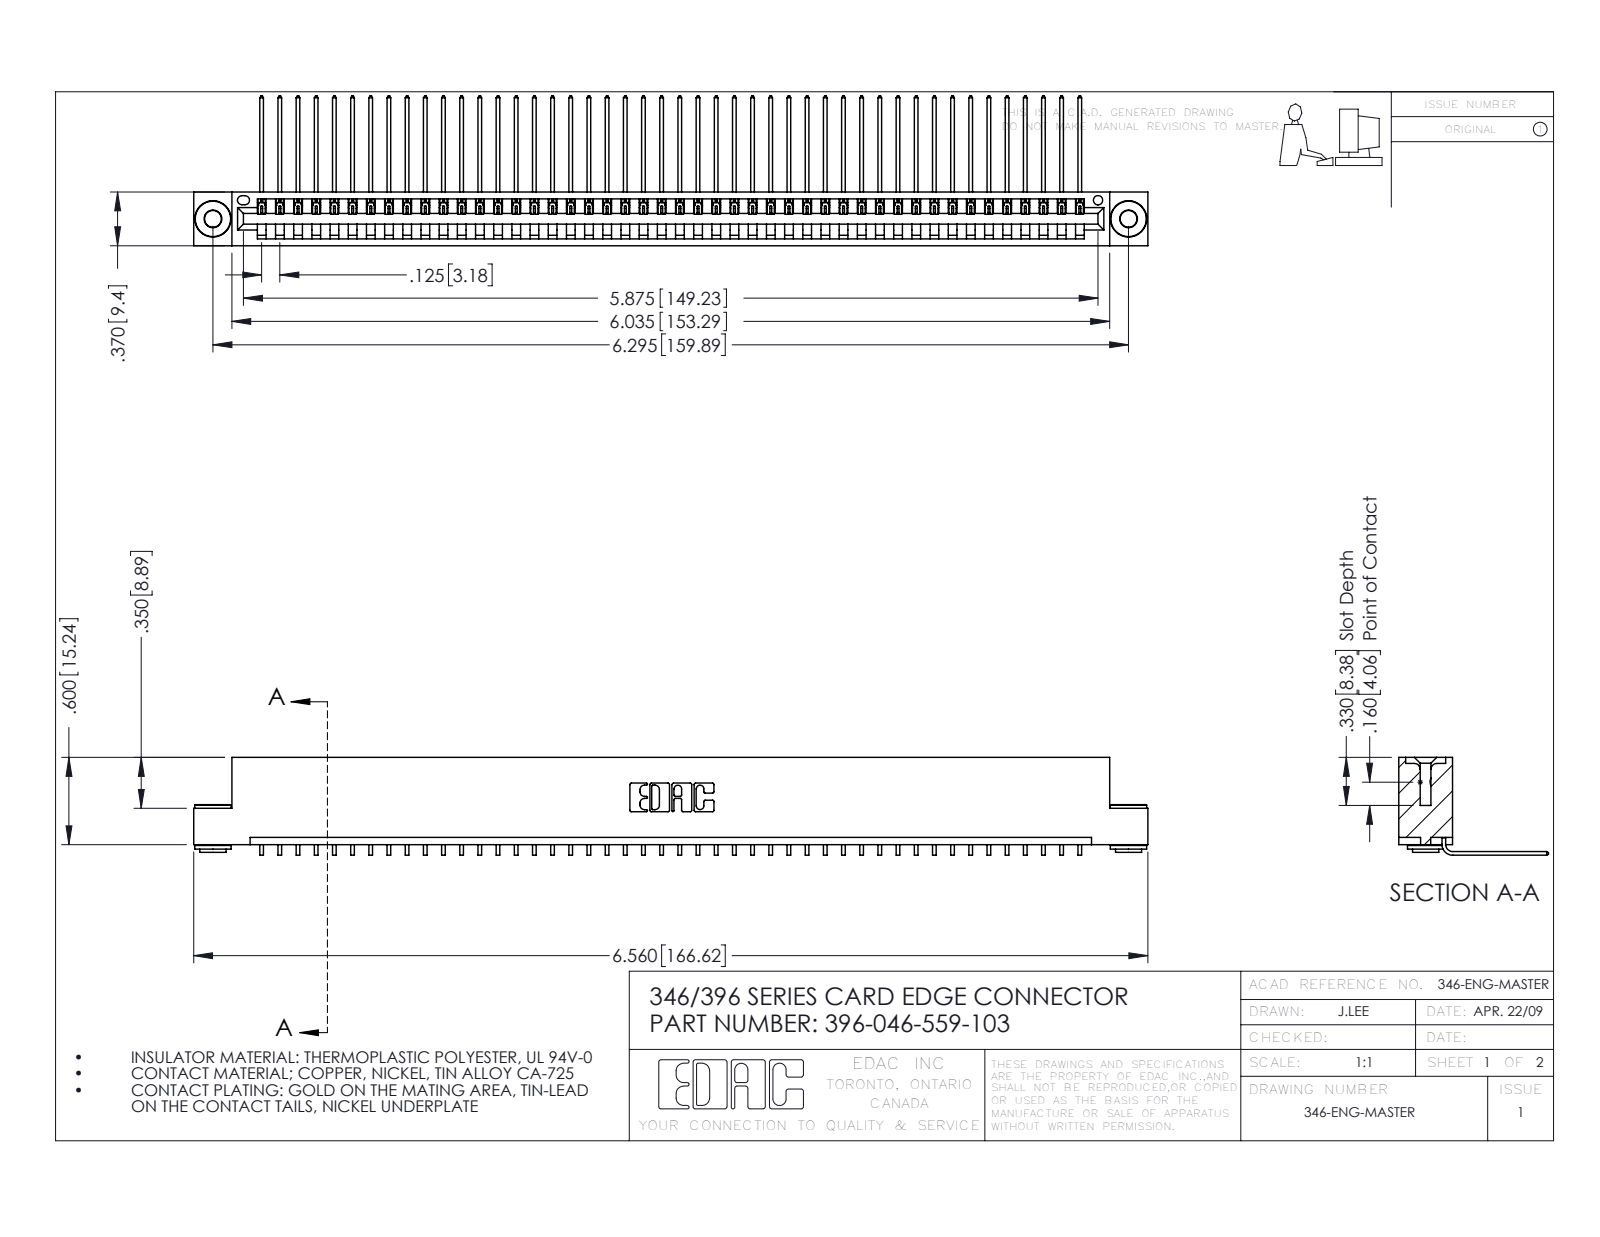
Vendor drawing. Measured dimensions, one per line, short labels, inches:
name: 346 Part_Flush Mounting Lugs - 0.156 Dia-TH; 396-046-559-103; 345-250-002_345-250-002-102; 345-292-001_558 559 Tail - 1
written by: SolidWorks 2016 (CONFIG_CONTROL_DESIGN)
unit: in
bodies: 49 solids, 2920 faces (2018 planar, 894 cylindrical, 8 other)
size: 6.56 × 1.03 × 0.673
volume: 0.986 in³; area: 33.11 in²
holes: 2× ⌀0.116, 2× ⌀0.156, 1× ⌀0.064
bosses: 2× ⌀0.25, 2× ⌀0.18, 2× ⌀0.136
rounds: 92× R0.006, 22× R0.01, 6× R0.007, 6× R0.031, 3× R0.026, 2× R0.031, 2× R0.04, 1× R0.014
face distances: 0.048, 0.322, 0.37, 0.25, 0.025, 0.072, 0.298, 0.148, 0.222, 0.1
hole spacings: 0.246, 6.086, 6.295
